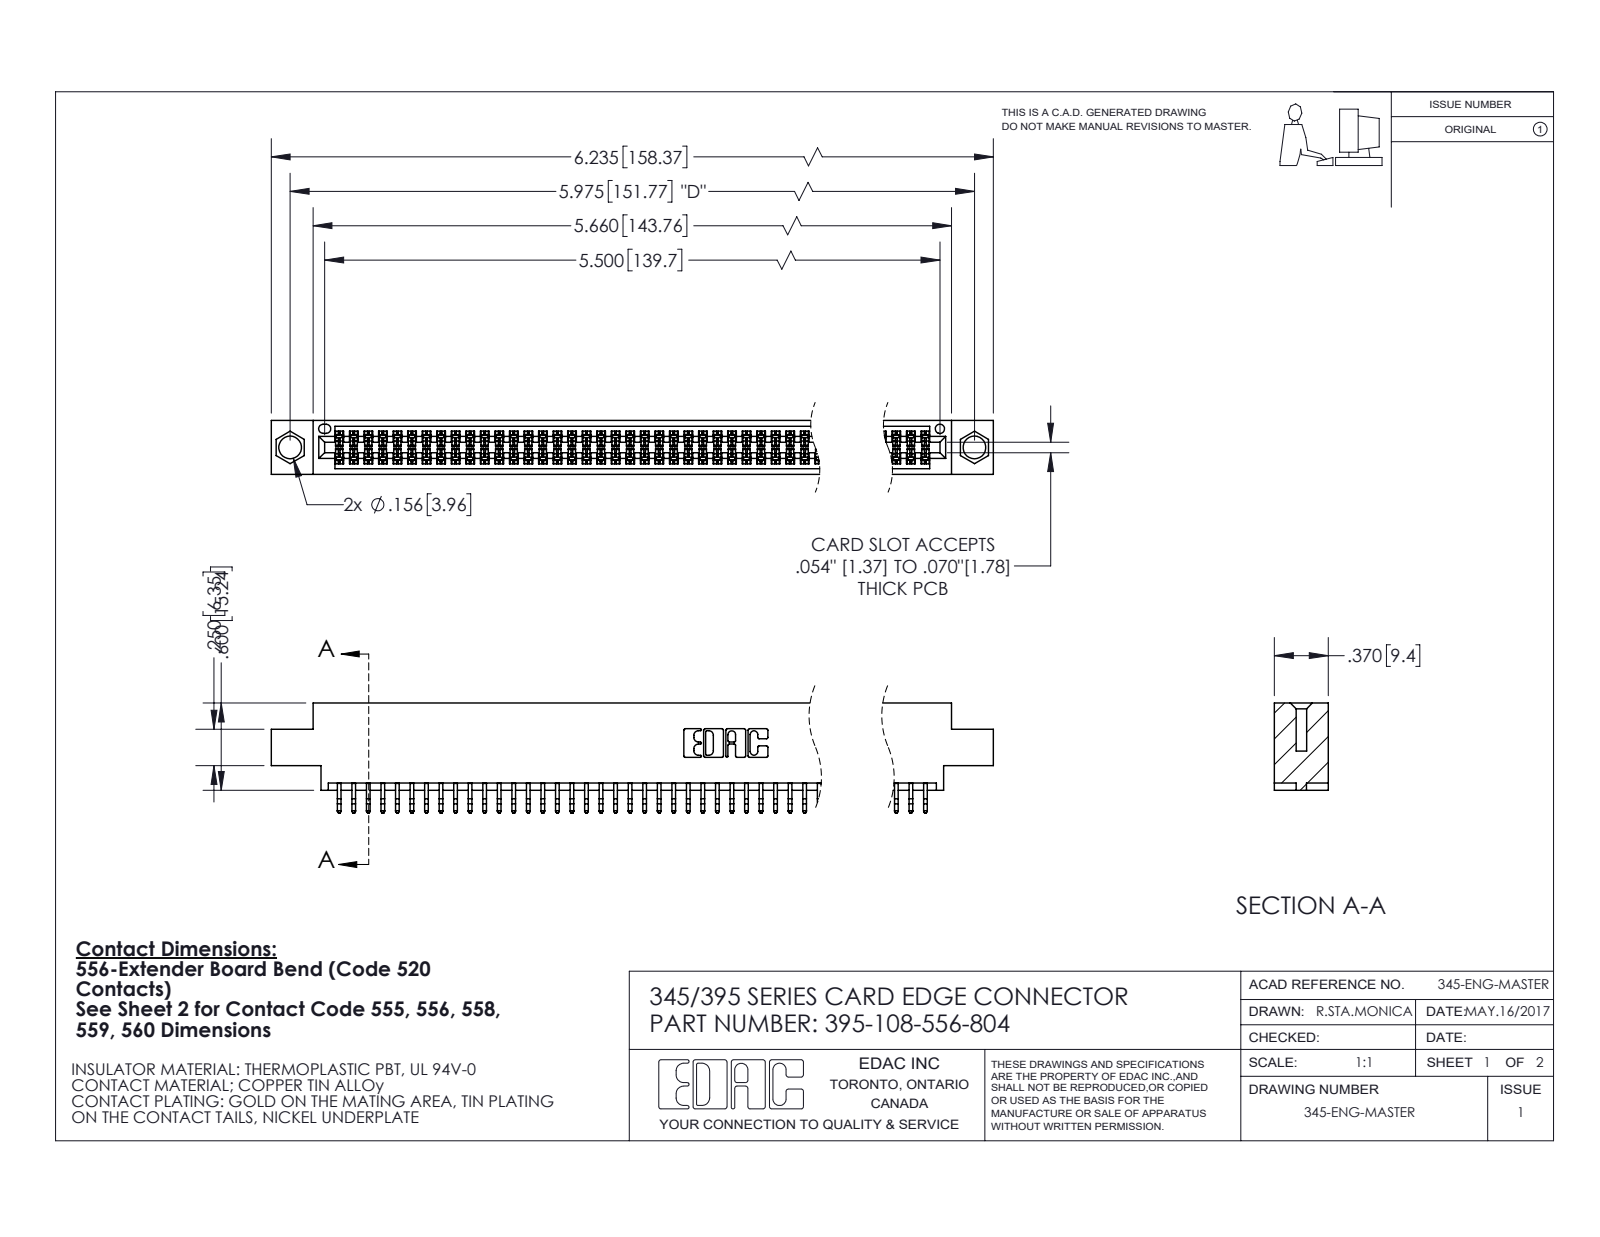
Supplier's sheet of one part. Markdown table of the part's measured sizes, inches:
| quantity | value |
| --- | --- |
| part name | 345-292-001_556 Tail; 395-108-556-804; 345 Part_0.170 Offset - 0.156 Dia-TI |
| STEP written by | SolidWorks 2020 (CONFIG_CONTROL_DESIGN) |
| units | inches |
| bodies | 109 solids, 6192 faces (4094 planar, 2098 cylindrical, 0 other) |
| overall size | 6.235 × 0.757 × 0.37 |
| volume | 0.932 in³ |
| surface area | 35.2 in² |
| round holes (diameter × count) | 0.156 × 2, 0.064 × 1 |
| partial cylindrical surfaces (radius × count) | 0.006 × 216, 0.01 × 22, 0.007 × 6, 0.031 × 6, 0.026 × 3, 0.01 × 2, 0.014 × 2, 0.019 × 2 |
| main face-to-face distances | 0.072, 0.298, 0.37, 0.025, 0.2, 0.098, 0.272, 0.225, 0.175, 0.149 |
| hole center spacings | 0.27, 5.739, 5.975 |
